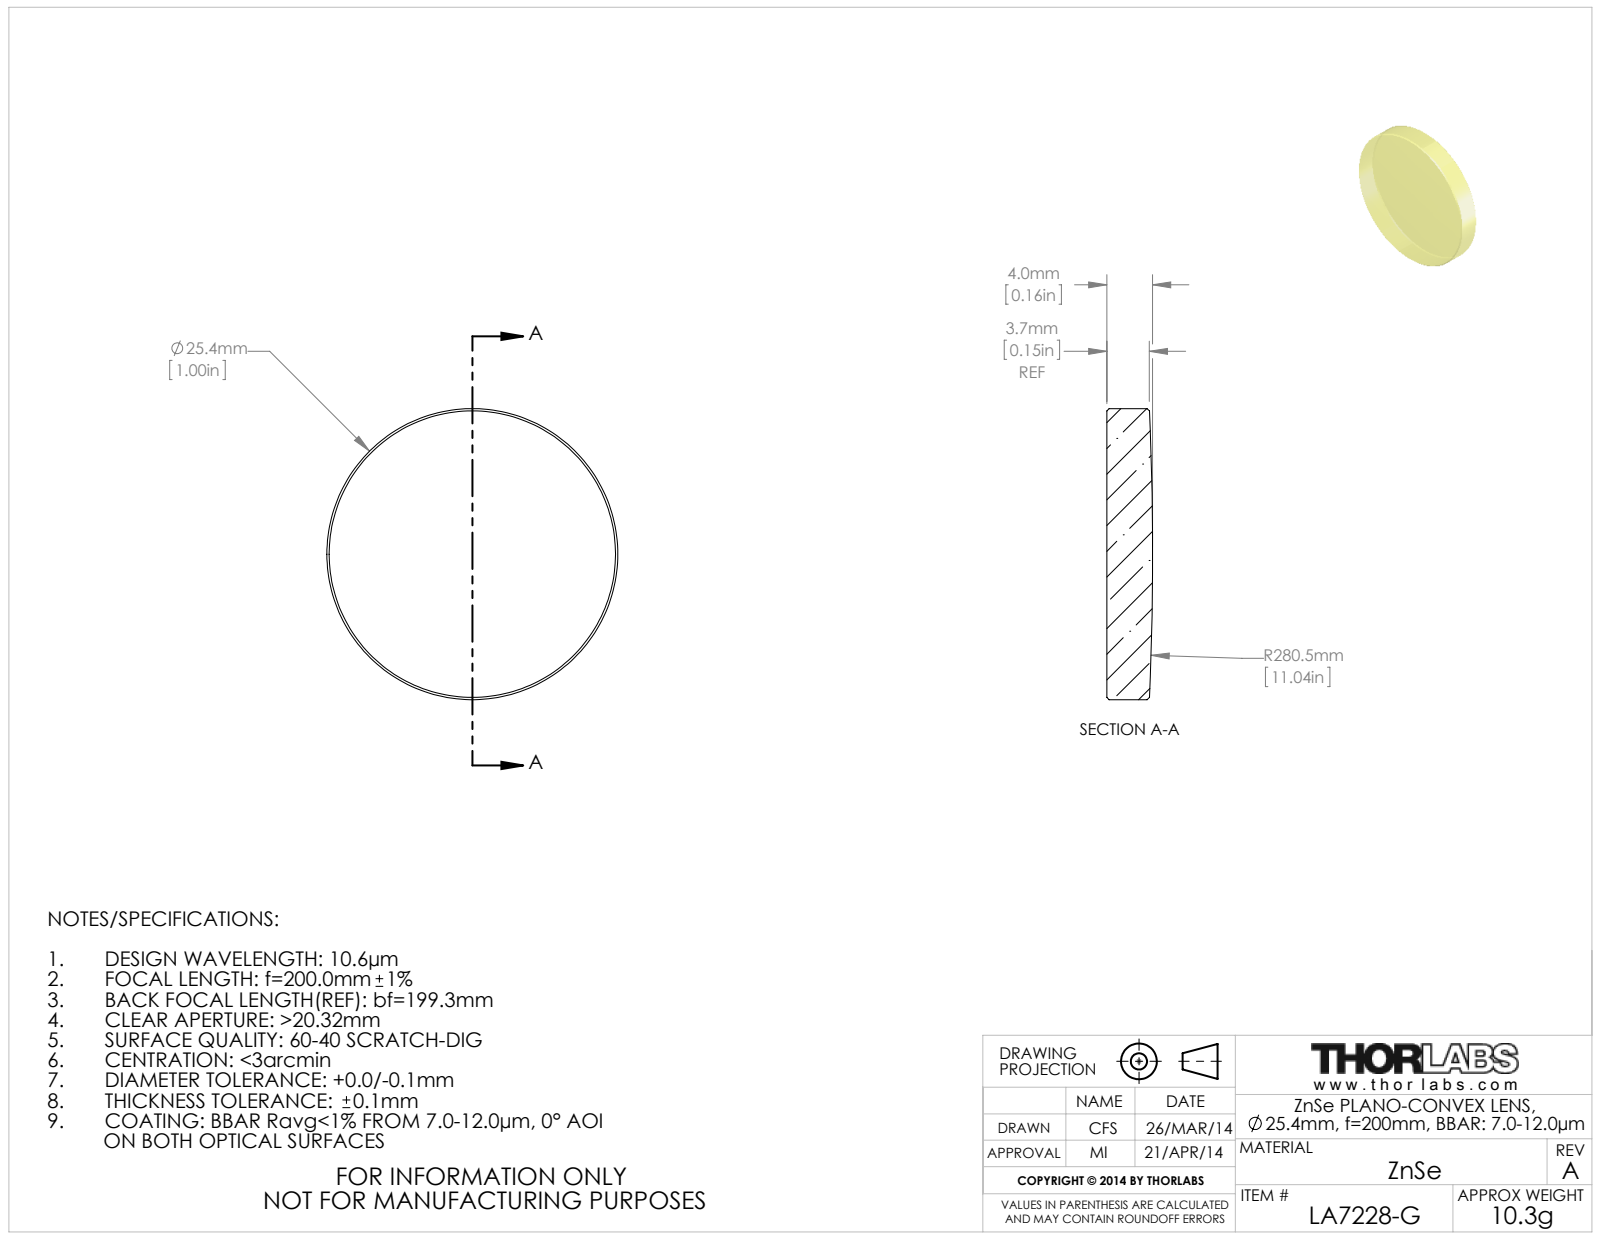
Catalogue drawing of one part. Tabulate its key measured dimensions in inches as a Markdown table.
| quantity | value |
| --- | --- |
| part name | TTN023917-E0W |
| STEP written by | SolidWorks 2012 (CONFIG_CONTROL_DESIGN) |
| units | inches |
| bodies | 1 solid, 9 faces (1 planar, 2 cylindrical, 6 other) |
| overall size | 1 × 1 × 0.157 |
| volume | 0.119 in³ |
| surface area | 2.002 in² |
| round bosses / shafts (diameter × count) | 1 × 1 |
